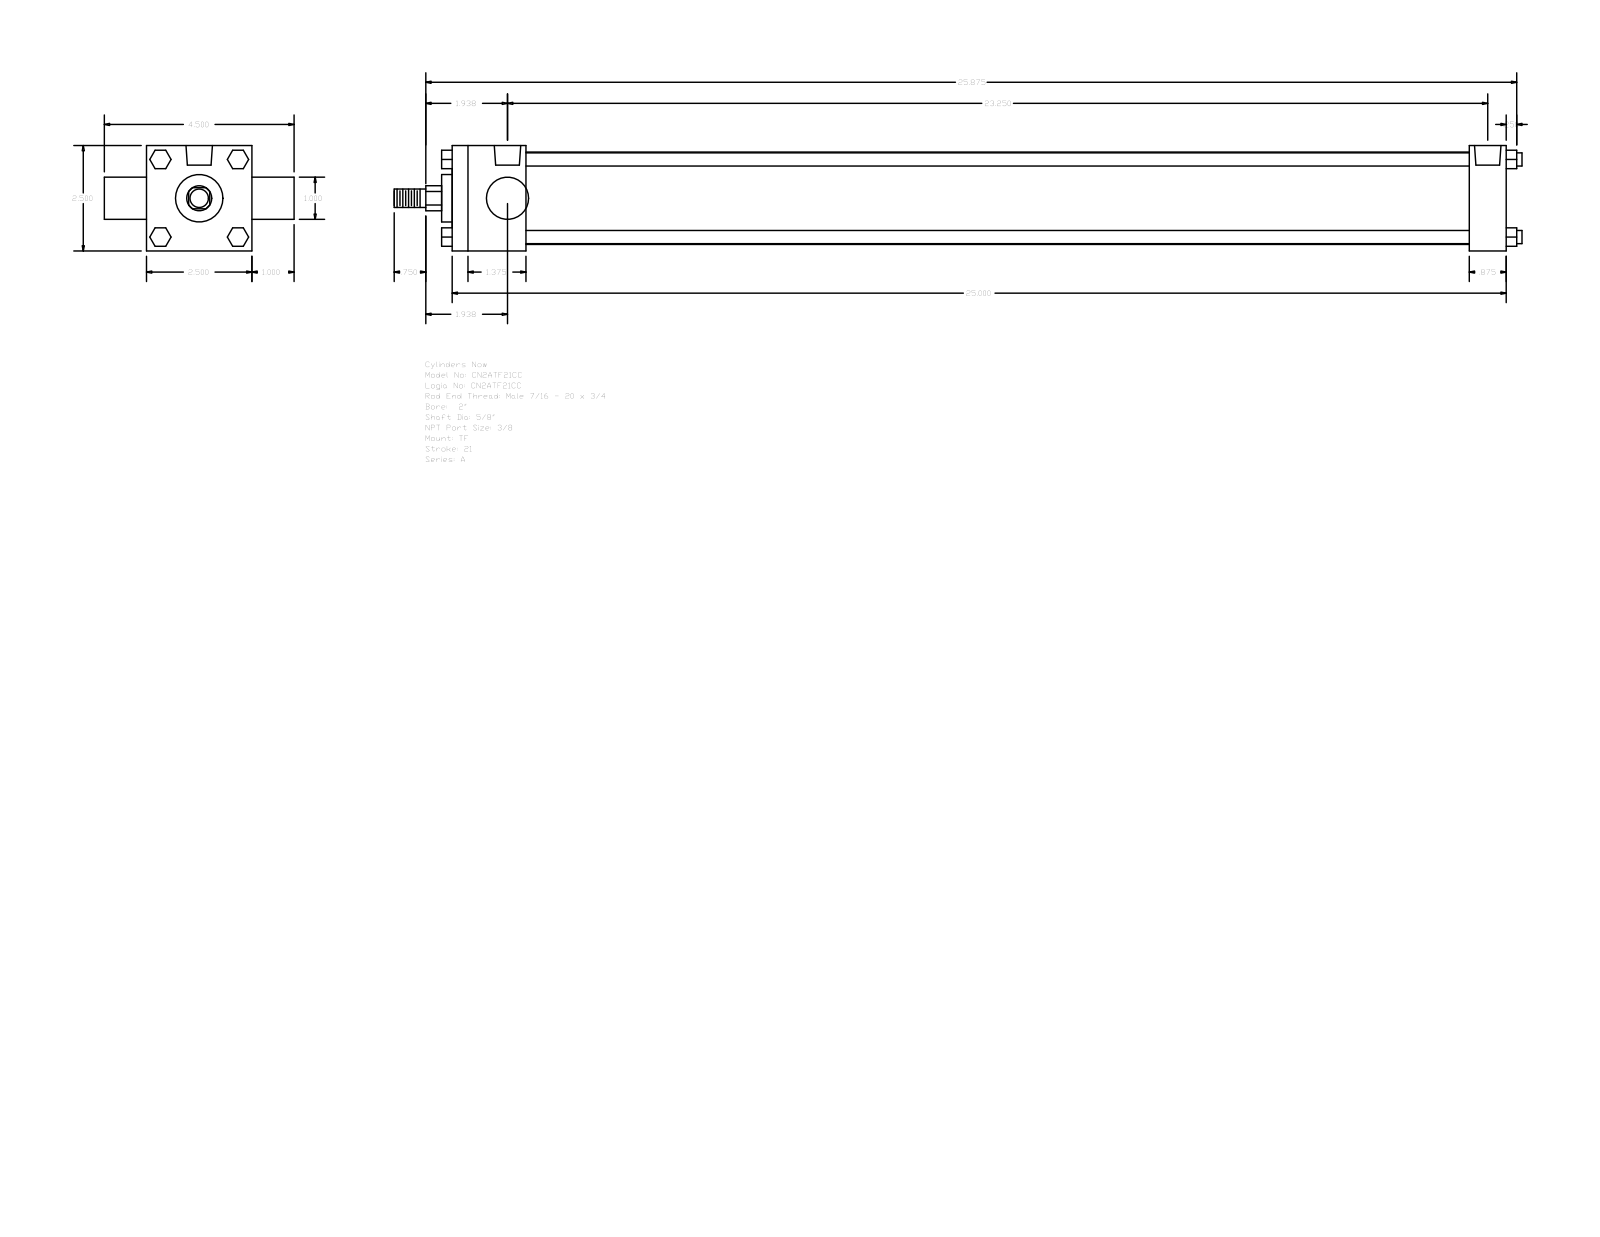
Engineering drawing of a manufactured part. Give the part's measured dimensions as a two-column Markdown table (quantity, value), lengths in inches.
| quantity | value |
| --- | --- |
| part name | A_TF__0200_0.625 |
| STEP written by | GSSL Pune (CONFIG_CONTROL_DESIGN) |
| units | inches |
| bodies | 0 solids, 120 faces (92 planar, 28 cylindrical, 0 other) |
| overall size | 26.75 × 4.5 × 2.5 |
| round holes (diameter × count) | 0.219 × 3, 0.627 × 2 |
| round bosses / shafts (diameter × count) | 0.313 × 4, 2.19 × 1, 1.125 × 1, 1 × 1, 0.625 × 1, 0.437 × 1 |
| partial cylindrical surfaces (radius × count) | 0.297 × 1 |
| main face-to-face distances | 2.5, 25, 1.75, 24.125, 22.375, 23.25, 0.875, 1, 3.5, 0.25 |
| hole center spacings | 0.156, 0.157, 22.937, 23.093, 23.094, 23.25 |
